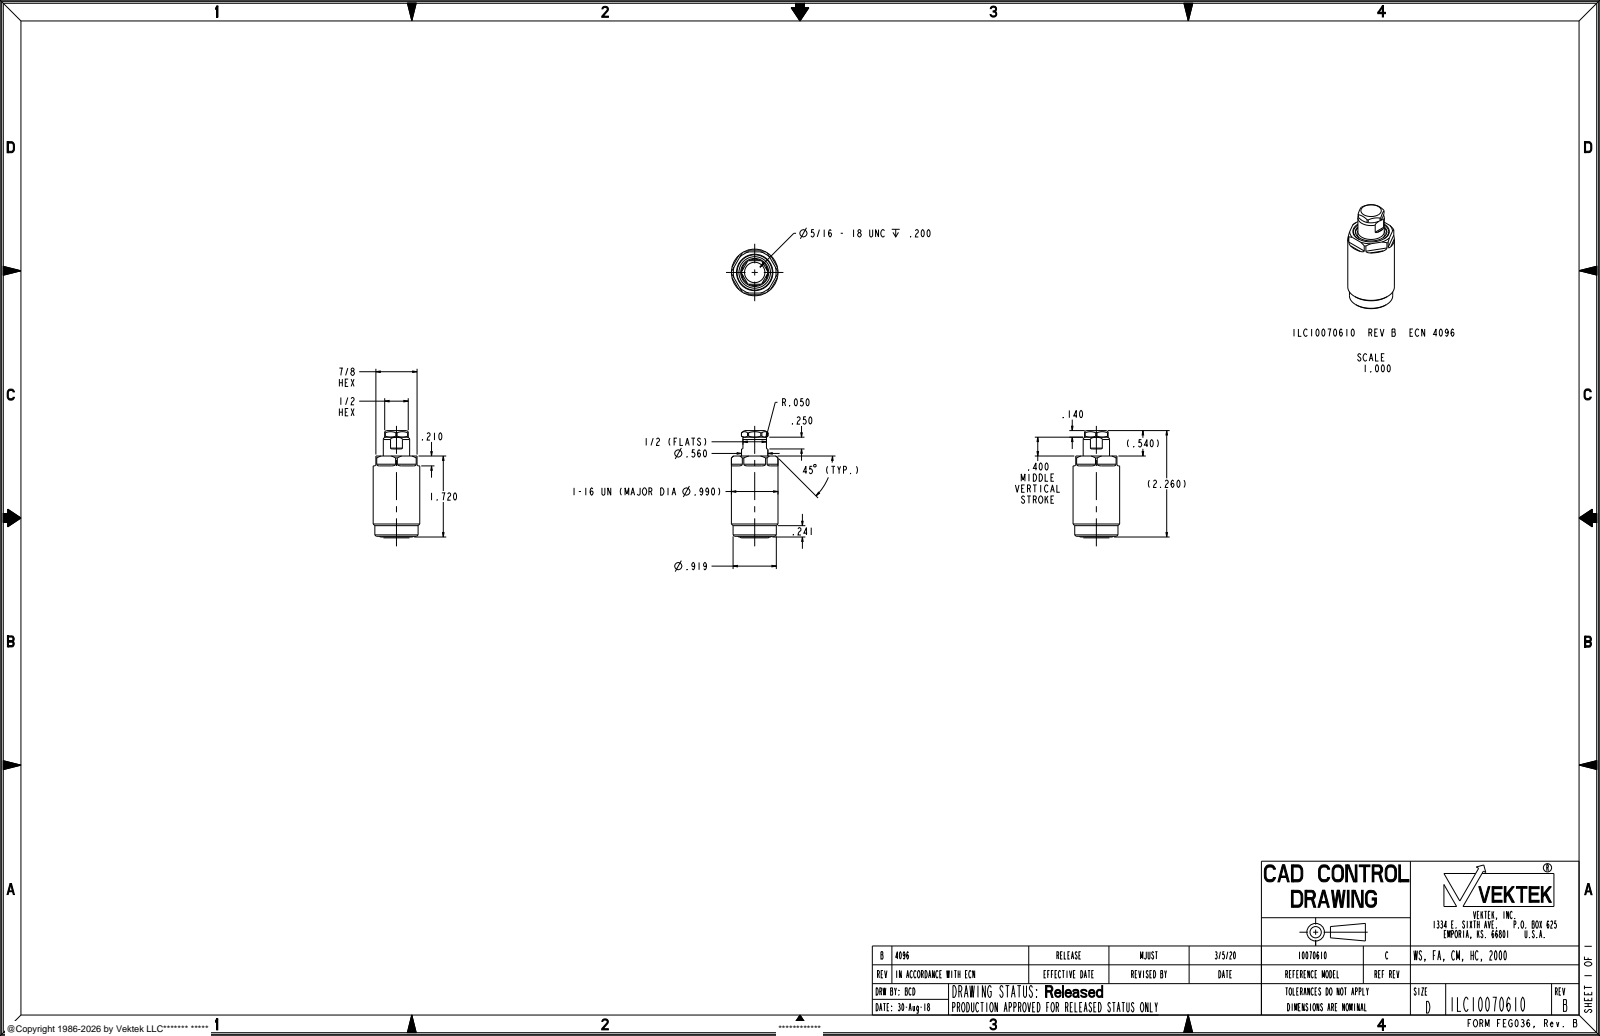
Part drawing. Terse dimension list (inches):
name: ILC10070610
written by: PRO/ENGINEER BY PARAMETRIC TECHNOLOGY CORPORATION, 2013320 (AUTOMOTIVE_DESIGN)
unit: in
bodies: 1 solid, 96 faces (34 planar, 32 cylindrical, 30 other)
size: 2.278 × 0.99 × 0.99
volume: 1.361 in³; area: 8.644 in²
holes: 1× ⌀0.188, 1× ⌀0.271, 1× ⌀0.625, 1× ⌀0.67
bosses: 1× ⌀0.99, 1× ⌀0.919, 1× ⌀0.75, 1× ⌀0.56, 1× ⌀0.313
rounds: 6× R0.036, 2× R0.018, 1× R0.281
face distances: 0.875, 0.037, 1.668, 1.705, 0.187, 0.687, 0.2, 2.245, 2.208, 0.54
